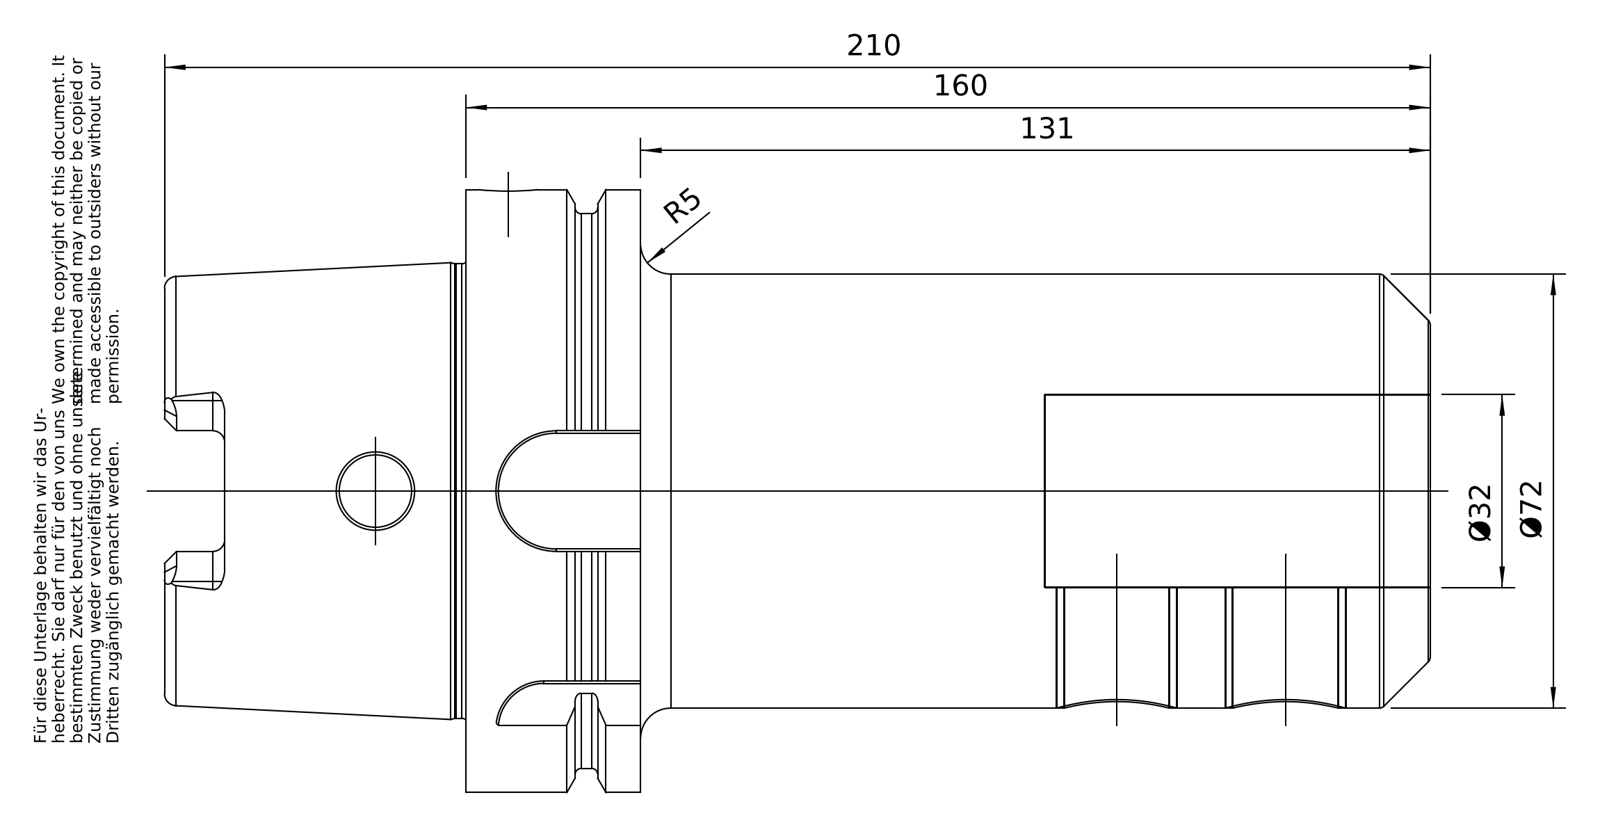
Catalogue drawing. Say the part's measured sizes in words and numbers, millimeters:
The part is named "A100-002-32". Its 3-D file was written by "PRO/ENGINEER BY PARAMETRIC TECHNOLOGY CORPORATION, 2010430 (CONFIG_CONTROL_DESIGN)". It is 1 solid with 184 faces: 50 planar, 59 cylindrical and 75 other. Overall it measures 210 by 100 by 100 millimeters. Its volume is 720 854 cubic millimeters and its surface area 88 599 square millimeters. Round holes: 2 of diameter 17.5, 2 of diameter 20, 1 of diameter 10, 1 of diameter 12, 1 of diameter 22.5, 1 of diameter 24, 1 of diameter 24.32, 1 of diameter 24.5, 1 of diameter 32, 1 of diameter 53, 1 of diameter 63. Round bosses or shafts: 1 of diameter 100, 1 of diameter 92, 1 of diameter 75.36, 1 of diameter 72. Partial cylindrical surfaces (rounded edges, fillets, slot ends): 6 of radius 2, 4 of radius 5, 1 of radius 8, 1 of radius 10, 1 of radius 11. The main face-to-face distances are 29, 131, 160, 12.5, 16.5, 147.5, 64, 50, 62.5, 79. The hole center spacings are 28, 101, 129.
